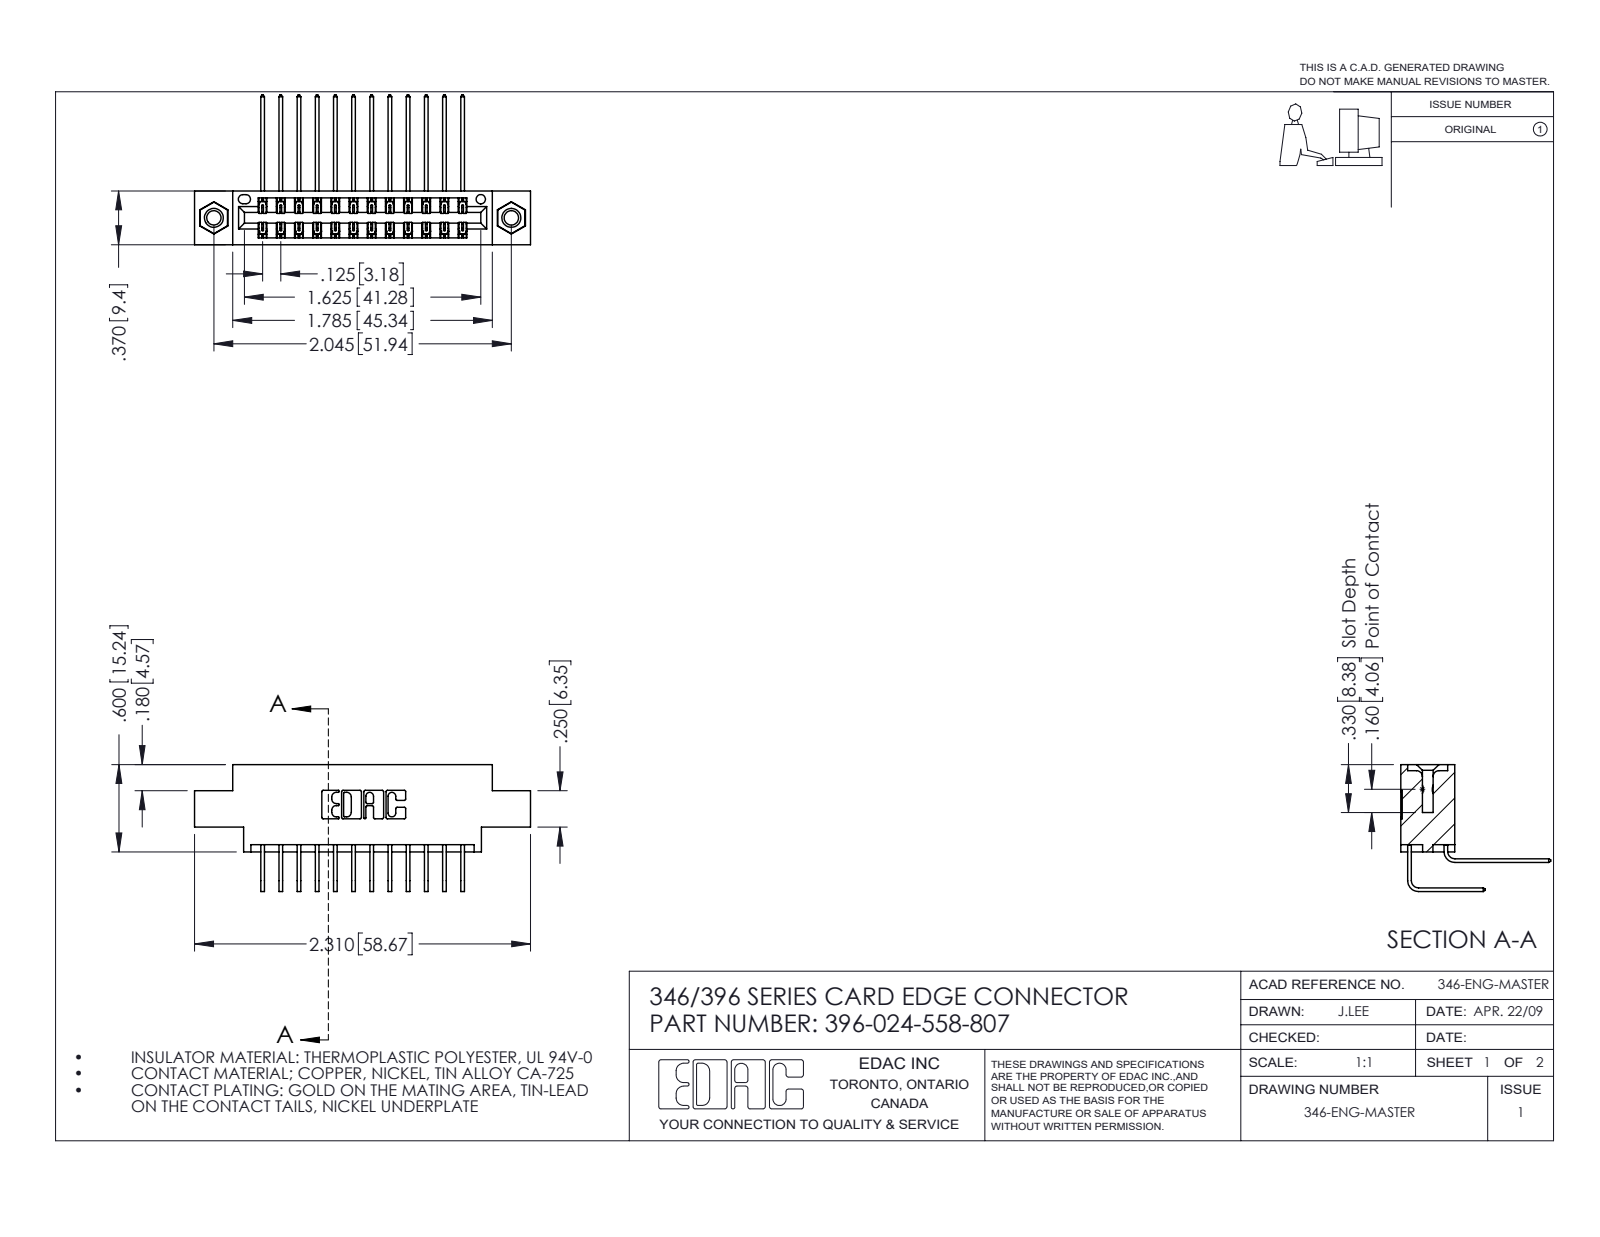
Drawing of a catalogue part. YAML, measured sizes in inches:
part_name: "346 Part_0.170 Offset - 0.156 Dia-TI; 345-250-001_345-250-005-103; 345-292-001_558 Tail - 2; 345-292-001_558 559 Tail - 1 (+1 more)"
step_written_by: "SolidWorks 2016 (CONFIG_CONTROL_DESIGN)"
units: inches
bodies: {solids: 27, faces: 1482, planar: 1000, cylindrical: 466, other: 16}
overall_size: [2.31, 1.03, 0.873]
volume: 0.333
surface_area: 12.26
round_holes:
  - {diameter: 0.098, count: 2}
  - {diameter: 0.125, count: 2}
  - {diameter: 0.156, count: 2}
  - {diameter: 0.064, count: 1}
round_bosses_or_shafts:
  - {diameter: 0.155, count: 2}
partial_cylinders:
  - {radius: 0.006, count: 36}
  - {radius: 0.01, count: 22}
  - {radius: 0.007, count: 6}
  - {radius: 0.031, count: 6}
  - {radius: 0.026, count: 3}
  - {radius: 0.014, count: 2}
  - {radius: 0.022, count: 2}
  - {radius: 0.024, count: 2}
face_to_face_distances: [0.048, 0.322, 0.25, 0.37, 0.025, 0.072, 0.298, 0.222, 0.148, 0.275]
hole_center_spacings: [0.246, 1.839, 2.045]
